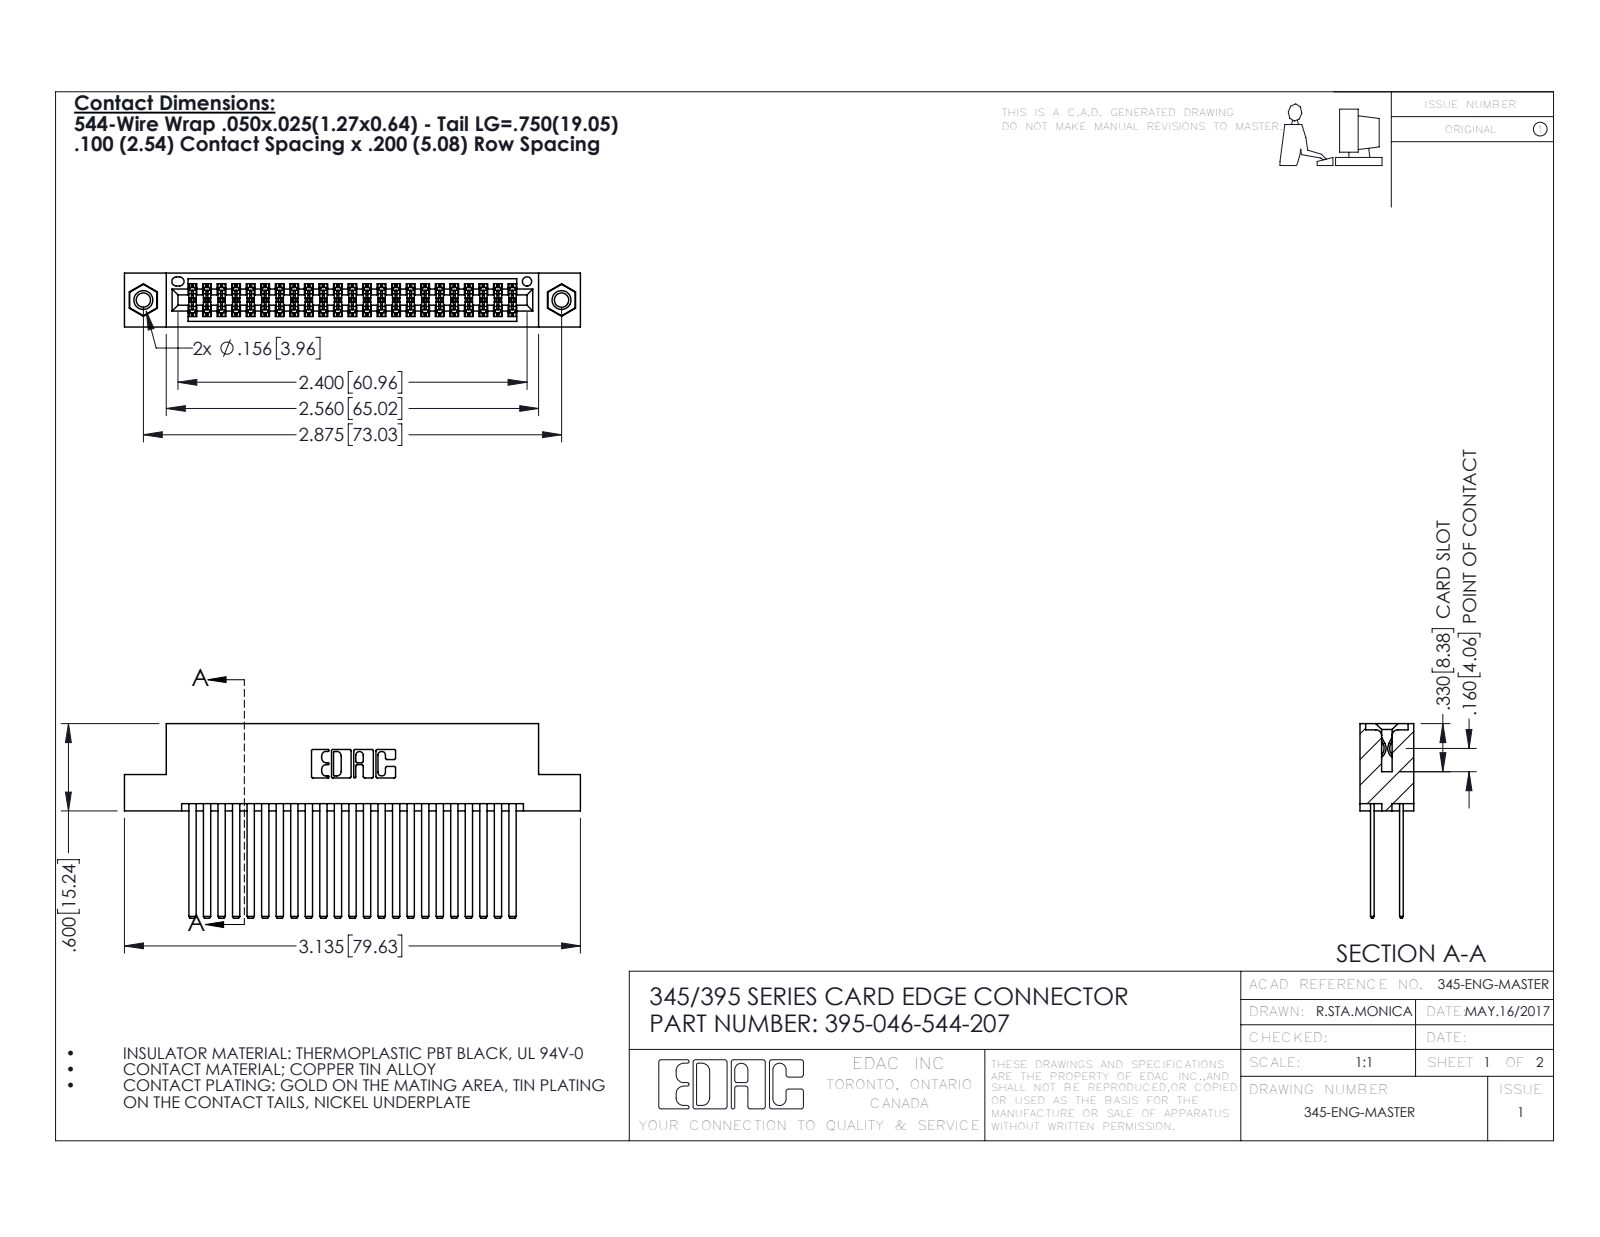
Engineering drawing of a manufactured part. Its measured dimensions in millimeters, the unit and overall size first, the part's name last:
Units: millimetres
Overall size (bounding box): 79.6 × 34 × 9.4
Round holes (diameter × count): ⌀2.5 ×2, ⌀3.2 ×2, ⌀4 ×2, ⌀1.6 ×1
Round bosses / shafts (diameter × count): ⌀3.9 ×2
Partial cylindrical surfaces — rounded edges, fillets, slot ends (radius × count): R0.2 ×69, R0.3 ×22, R0.2 ×6, R0.8 ×6, R0.7 ×3, R0.4 ×2, R0.5 ×2, R0.6 ×2
Main face-to-face distances: 5.1, 1.8, 7.6, 2.5, 6.9, 0.6, 5.7, 9.4, 4.4, 1.3
Hole centre spacings: 6.9, 67.1, 73
Volume: 8 190 mm³ · Surface area: 13 660 mm²
Bodies: 49 solids, 2210 faces (1446 planar, 748 cylindrical, 16 other)
Part name (STEP PRODUCT): 345-292-001_345-293-144; 345-250-001_345-250-005-103; 345 Part_Flush Mounting Lugs - 0.156 Dia-TI; 395-046-544-207
STEP written by: SolidWorks 2016 (CONFIG_CONTROL_DESIGN)
